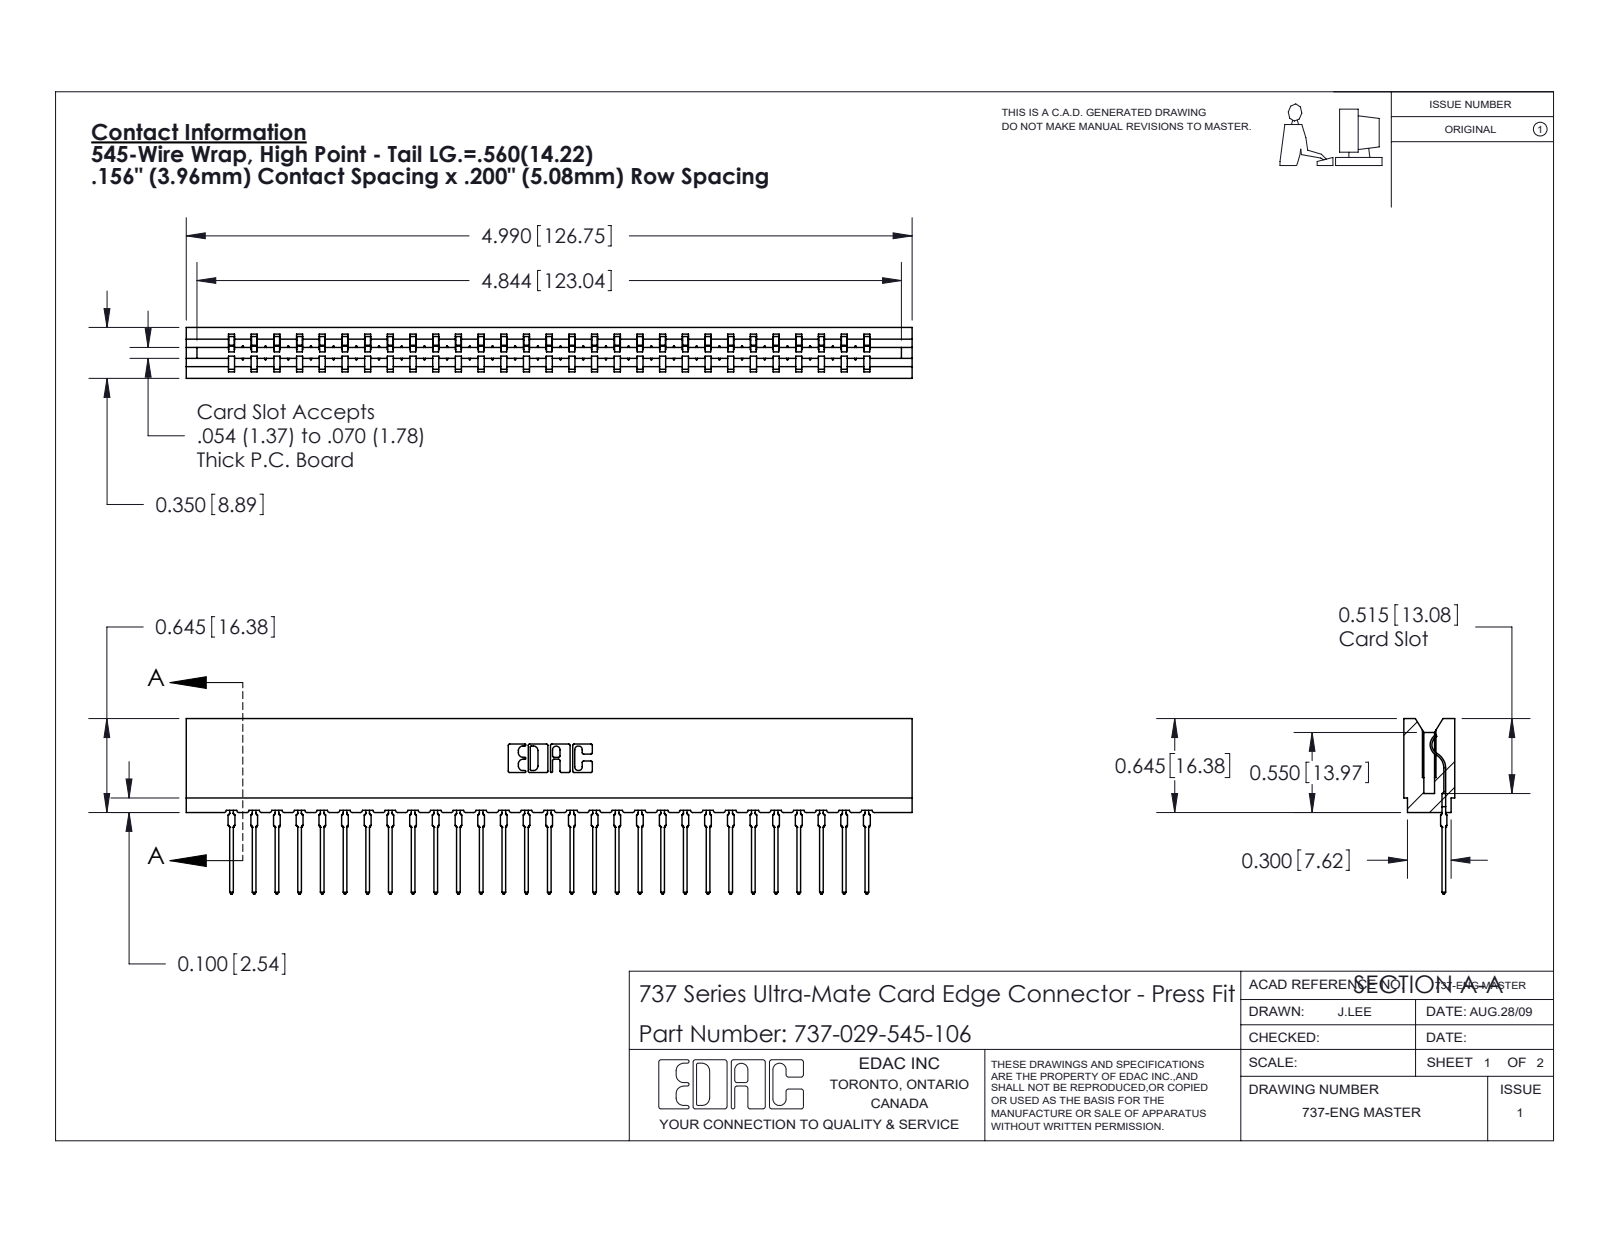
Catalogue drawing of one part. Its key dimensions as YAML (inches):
part_name: "745-292-001_545; 737 Part_Insulator Option - 06; 737-029-545-106"
step_written_by: "SolidWorks 2020 (CONFIG_CONTROL_DESIGN)"
units: inches
bodies: {solids: 30, faces: 3372, planar: 2027, cylindrical: 591, other: 754}
overall_size: [4.99, 1.206, 0.35]
volume: 0.757
surface_area: 26.2
partial_cylinders:
  - {radius: 0.015, count: 58}
  - {radius: 0.021, count: 58}
  - {radius: 0.01, count: 22}
  - {radius: 0.007, count: 6}
  - {radius: 0.031, count: 6}
  - {radius: 0.005, count: 4}
  - {radius: 0.011, count: 4}
  - {radius: 0.026, count: 3}
face_to_face_distances: [0.138, 0.212, 0.35, 0.074, 0.156, 0.624, 0.045, 0.305, 0.093, 0.167]
